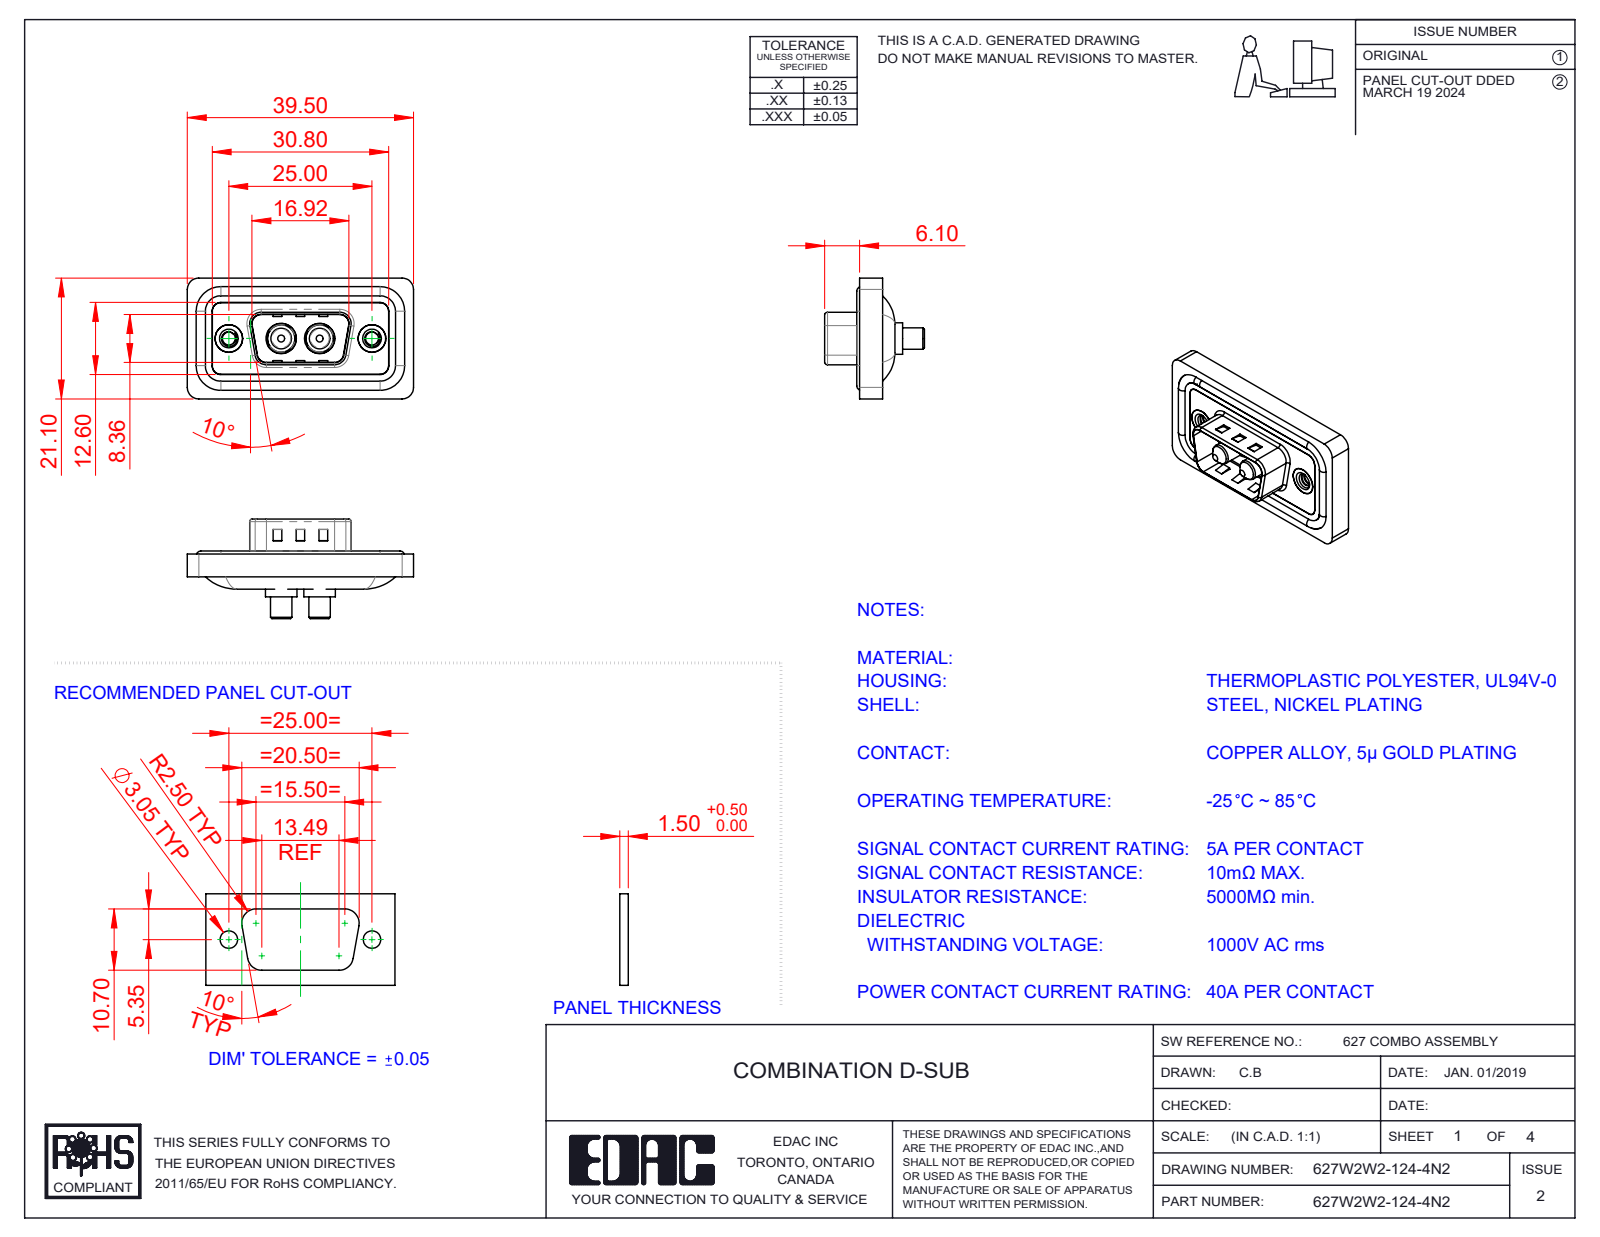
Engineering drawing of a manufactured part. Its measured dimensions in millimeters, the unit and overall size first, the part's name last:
Units: millimetres
Overall size (bounding box): 39.5 × 21.1 × 17.4
Round holes (diameter × count): ⌀2.26 ×2, ⌀4 ×2, ⌀4.8 ×2, ⌀4.85 ×2, ⌀5 ×2, ⌀5.3 ×2
Round bosses / shafts (diameter × count): ⌀1.6 ×4, ⌀5.5 ×2, ⌀5.2 ×2, ⌀4.9 ×2, ⌀4.75 ×2, ⌀3.75 ×2, ⌀3.6 ×2
Partial cylindrical surfaces — rounded edges, fillets, slot ends (radius × count): R1.5 ×22, R2 ×18, R0.5 ×8, R1.6 ×8, R0.25 ×4, R0.6 ×4, R0.65 ×4, R0.9 ×4
Main face-to-face distances: 0.4, 1.1, 2.9, 3.1, 0.5, 1.6, 1.5, 2.5, 4, 0.7
Hole centre spacings: 9.14, 15.86, 6.72, 25
Volume: 4 497 mm³ · Surface area: 7 006 mm²
Bodies: 11 solids, 489 faces (165 planar, 218 cylindrical, 106 other)
Part name (STEP PRODUCT): 627Combo Shell Rear_09 Contacts; 627Combo Housing_2W2; 627W2W2-124-4N2; 627Combo Threaded Rivet_2 (+3 more)
STEP written by: SolidWorks 2023 (CONFIG_CONTROL_DESIGN)
